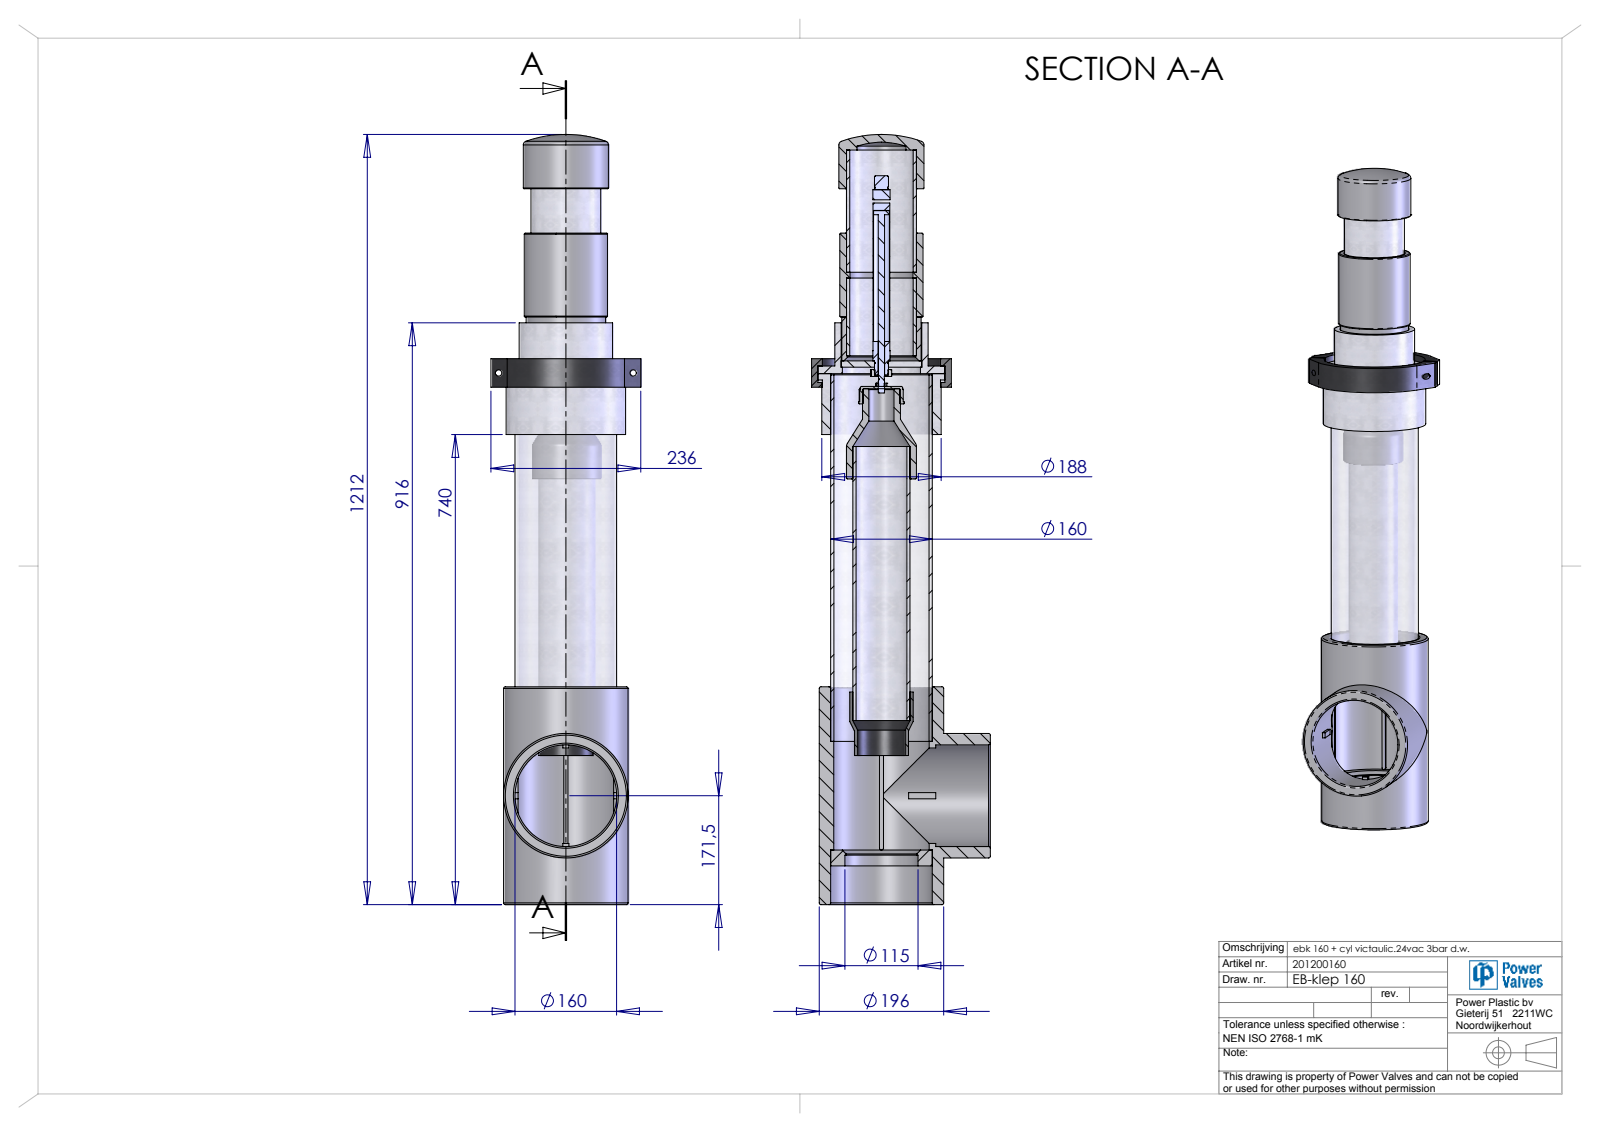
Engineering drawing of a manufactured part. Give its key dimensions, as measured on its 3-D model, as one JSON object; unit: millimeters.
{"part_name": "3_90_110; 2_01_160; 19226 DSNU-25-200-P-A---(0)_Standard; 216233-a001 (+8 more)", "step_written_by": "SolidWorks 2014 (AUTOMOTIVE_DESIGN)", "units": "millimeters", "bodies": {"solids": 23, "faces": 513, "planar": 158, "cylindrical": 212, "other": 143}, "overall_size": [1212.4, 281.5, 236], "volume_mm3": 10510000, "surface_area_mm2": 2365000, "round_holes": [[10, 2], [160, 2], [8.57, 1], [8.65, 1], [20.38, 1], [25, 1], [39.61, 1], [56.66, 1], [75, 1], [77, 1], [80, 1], [90, 1]], "round_bosses_or_shafts": [[196, 2], [188, 1], [147, 1], [134, 1], [131, 1], [125, 1], [85, 1], [71.61, 1]], "partial_cylinders_radius": [[1.68, 24], [3.2, 4], [0.3, 2], [0.4, 2], [110, 1]], "face_to_face_distances": [10, 12, 20, 33.5, 11.5, 8, 2, 21.5, 31.5, 41.5], "hole_center_spacings": [673.89, 212]}
